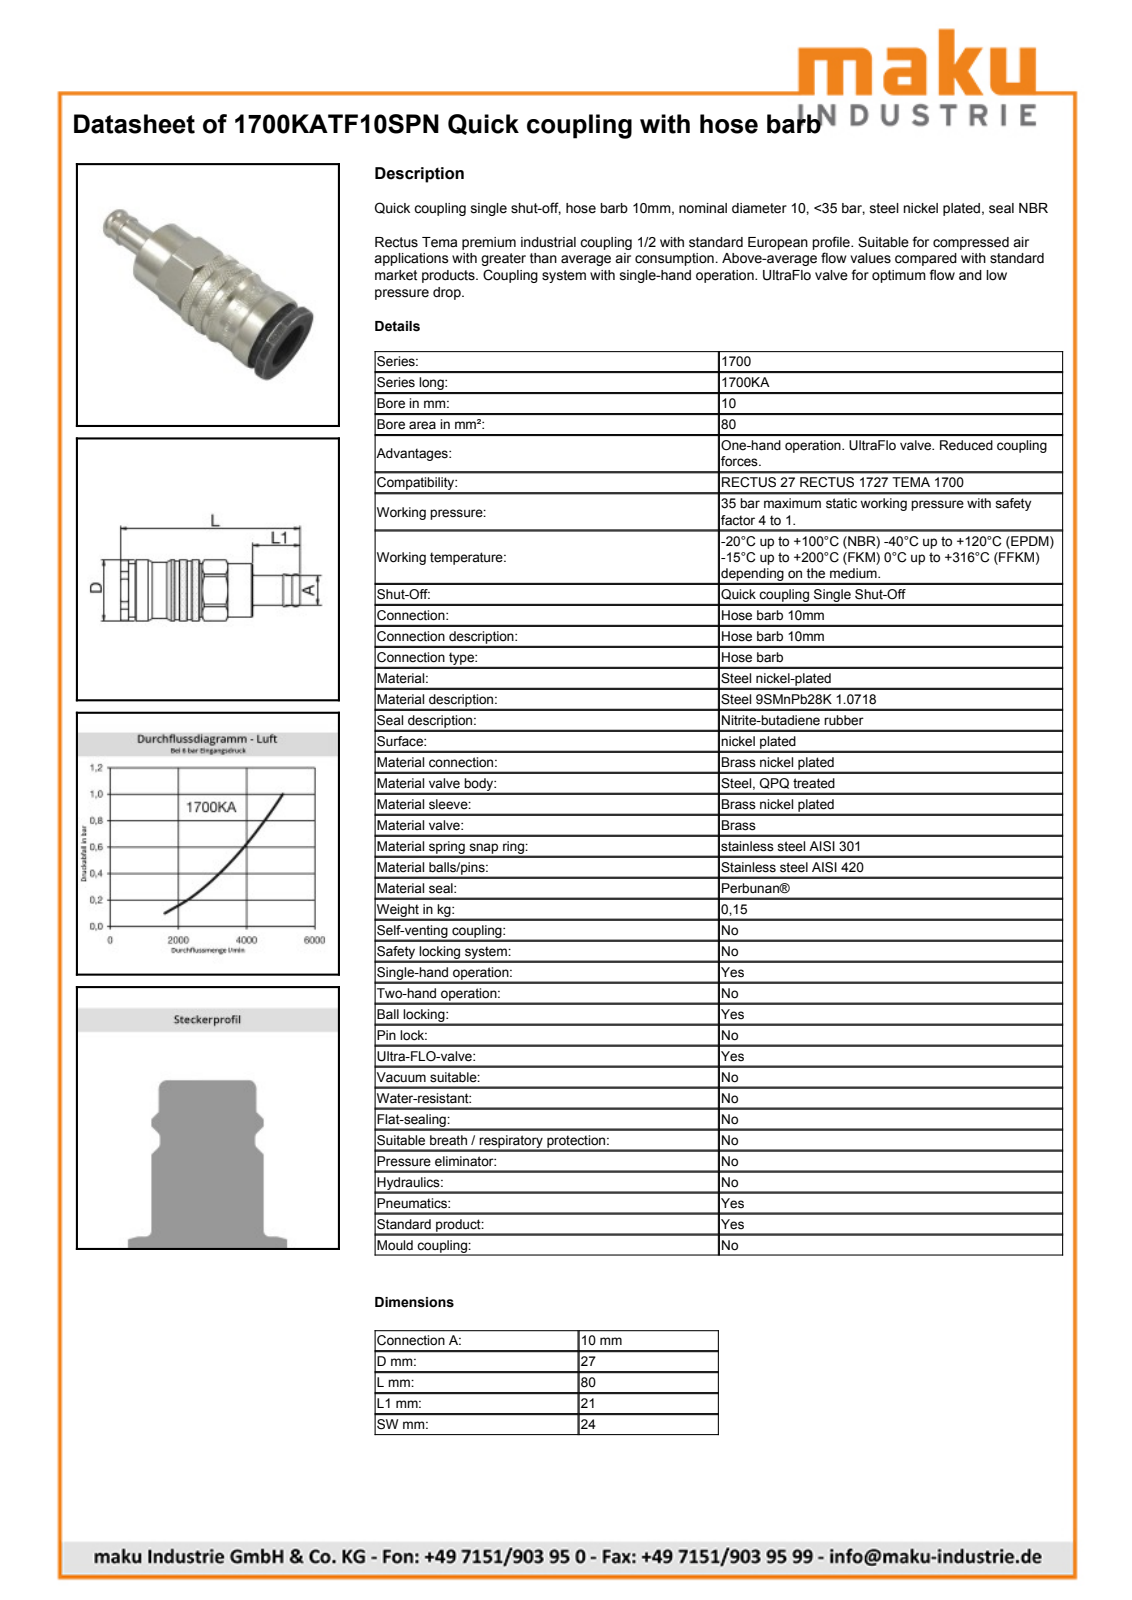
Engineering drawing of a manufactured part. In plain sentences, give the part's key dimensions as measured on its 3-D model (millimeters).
The part is named "D103703". Its 3-D file was written by "Autodesk Inventor 2011 (AUTOMOTIVE_DESIGN)". It is 2 solids with 664 faces: 196 planar, 93 cylindrical and 375 other. Overall it measures 79.64 by 27.05 by 26.8 millimeters. Its volume is 29 915 cubic millimeters and its surface area 12 230 square millimeters. Round holes: 1 of diameter 20.15, 1 of diameter 21.2, 1 of diameter 21.4, 1 of diameter 22.5, 1 of diameter 23.8, 1 of diameter 24. Round bosses or shafts: 1 of diameter 26.8, 1 of diameter 26, 1 of diameter 25, 1 of diameter 23.7, 1 of diameter 21.3, 1 of diameter 21, 1 of diameter 20.97, 1 of diameter 19.99. Partial cylindrical surfaces (rounded edges, fillets, slot ends): 1 of radius 12.4, 1 of radius 13.5, 1 of radius 13.53. The main face-to-face distances are 24, 58.64, 1, 25, 30.64, 28, 6.55, 24.09, 52.09, 79.64.
